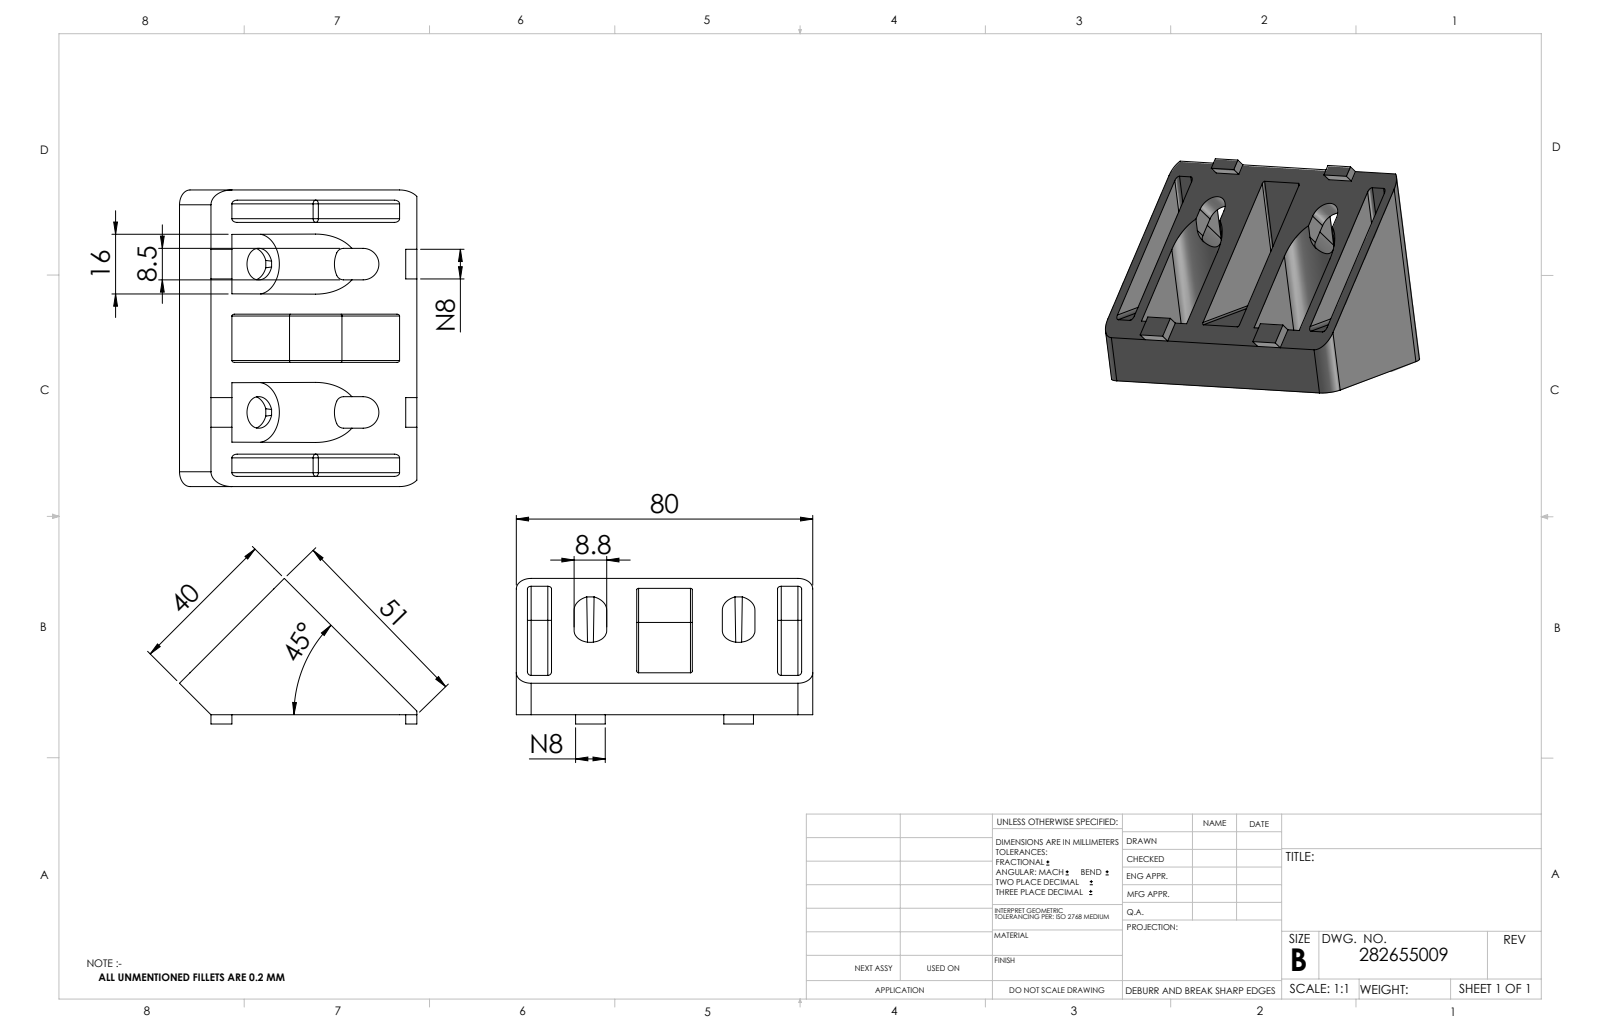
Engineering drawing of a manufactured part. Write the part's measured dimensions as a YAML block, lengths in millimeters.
part_name: "282655009_c_1"
step_written_by: "SolidWorks 2014 (CONFIG_CONTROL_DESIGN)"
units: millimeters
bodies: {solids: 1, faces: 137, planar: 73, cylindrical: 54, other: 10}
overall_size: [80, 53.06, 41.76]
volume: 61680
surface_area: 24020
partial_cylinders:
  - {radius: 1, count: 21}
  - {radius: 0.5, count: 12}
  - {radius: 2, count: 4}
  - {radius: 4, count: 4}
  - {radius: 4.25, count: 2}
  - {radius: 7.75, count: 2}
  - {radius: 8.1, count: 2}
face_to_face_distances: [40, 3, 80, 2.75, 24.75, 13, 8.75, 71.25, 77.25, 68.5]
